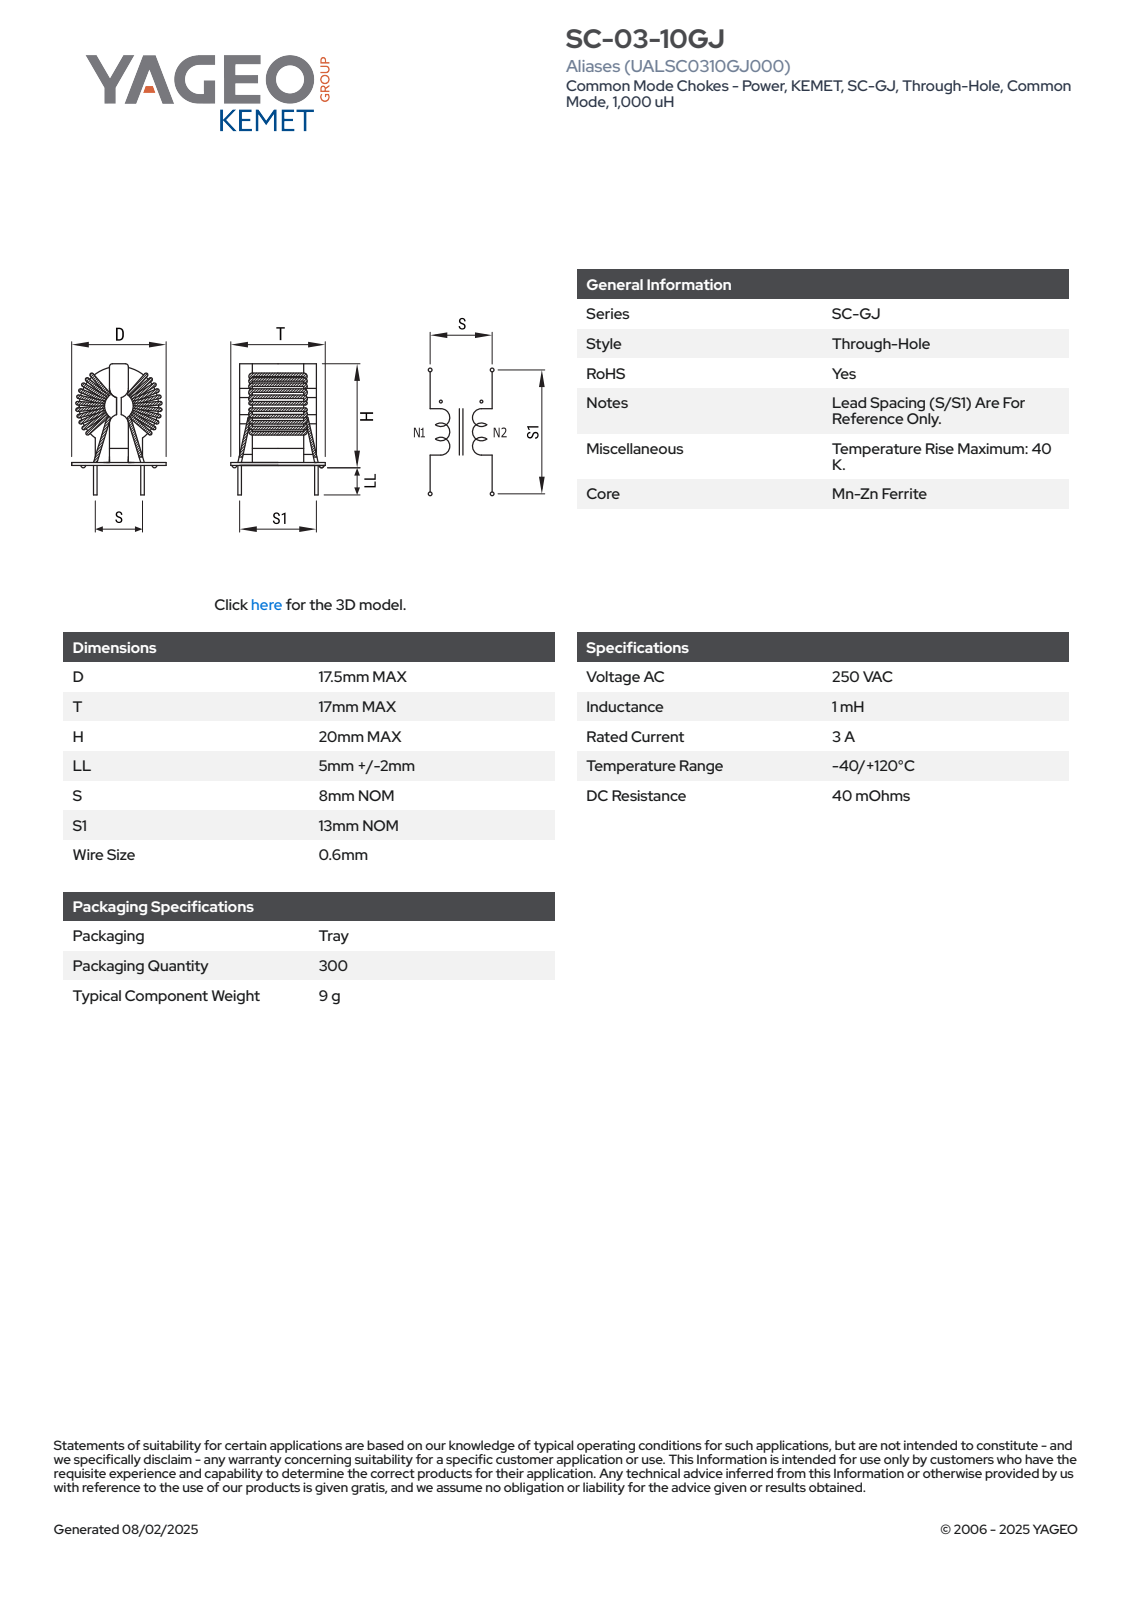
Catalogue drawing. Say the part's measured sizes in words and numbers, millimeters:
The part is named "SC-03-10GJ". Its 3-D file was written by "SolidWorks 2018 (AUTOMOTIVE_DESIGN)". It is 7 solids with 407 faces: 174 planar, 133 cylindrical and 100 other. Overall it measures 25 by 17.5 by 17 millimeters. Its volume is 3 478 cubic millimeters and its surface area 4 309 square millimeters. Round holes: 1 of diameter 7.6, 1 of diameter 13. Round bosses or shafts: 8 of diameter 0.6, 4 of diameter 1, 1 of diameter 13.9, 1 of diameter 12.85, 1 of diameter 12.7, 1 of diameter 7.25. Partial cylindrical surfaces (rounded edges, fillets, slot ends): 19 of radius 0.3, 16 of radius 0.5, 6 of radius 0.2, 4 of radius 1, 4 of radius 1.6, 2 of radius 0.6, 2 of radius 0.9, 2 of radius 2. The main face-to-face distances are 2, 1.4, 9.97, 3.2, 8.5, 1.03, 1.47, 1.2, 9.53, 11.
